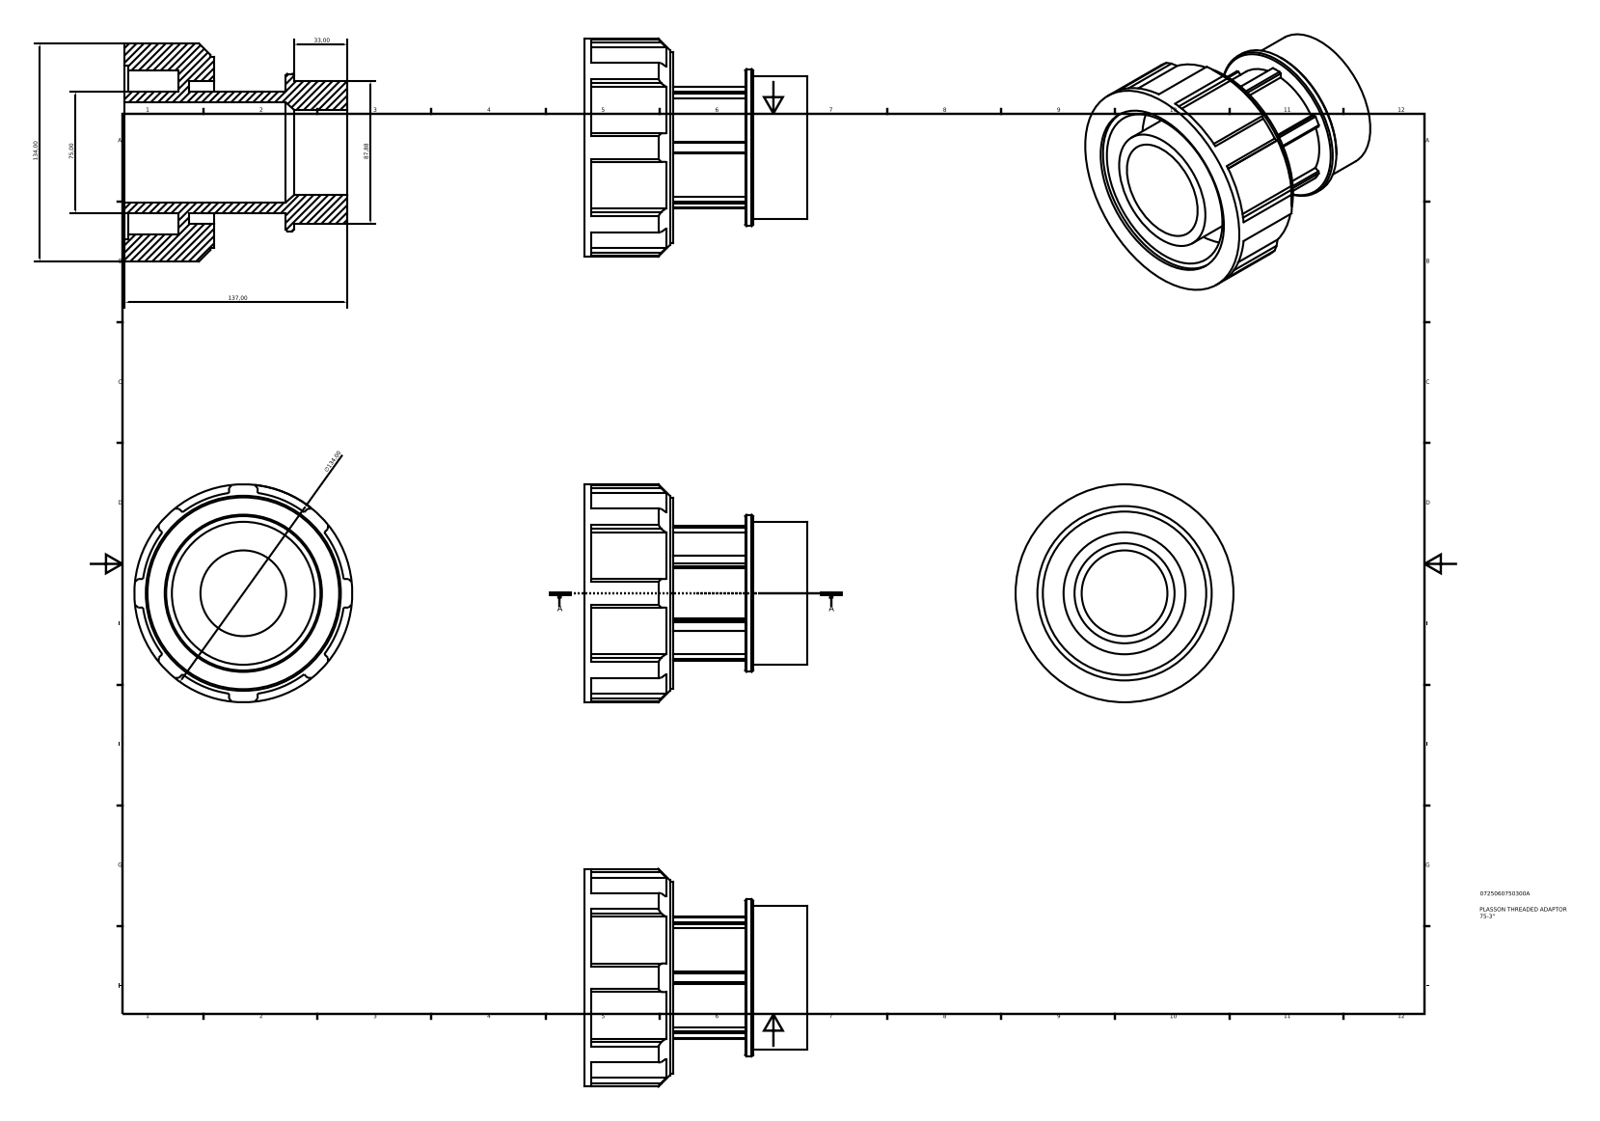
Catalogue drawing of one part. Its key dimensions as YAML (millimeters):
part_name: "0725060750300A"
step_written_by: "Autodesk Inventor 2015 (AUTOMOTIVE_DESIGN)"
units: millimeters
bodies: {solids: 1, faces: 108, planar: 74, cylindrical: 30, other: 4}
overall_size: [137, 134, 134]
volume: 619941
surface_area: 126791
round_holes:
  - {diameter: 52.73, count: 1}
  - {diameter: 61.52, count: 1}
  - {diameter: 87.75, count: 1}
  - {diameter: 100.5, count: 1}
  - {diameter: 107.2, count: 1}
round_bosses_or_shafts:
  - {diameter: 134, count: 1}
  - {diameter: 117.92, count: 1}
  - {diameter: 96.67, count: 1}
  - {diameter: 87.88, count: 1}
  - {diameter: 75, count: 1}
partial_cylinders:
  - {radius: 41.25, count: 1}
  - {radius: 62.31, count: 1}
face_to_face_distances: [54.8, 33, 104, 137, 82.2, 21.8, 99.05, 66.05, 44.25, 37.95]
